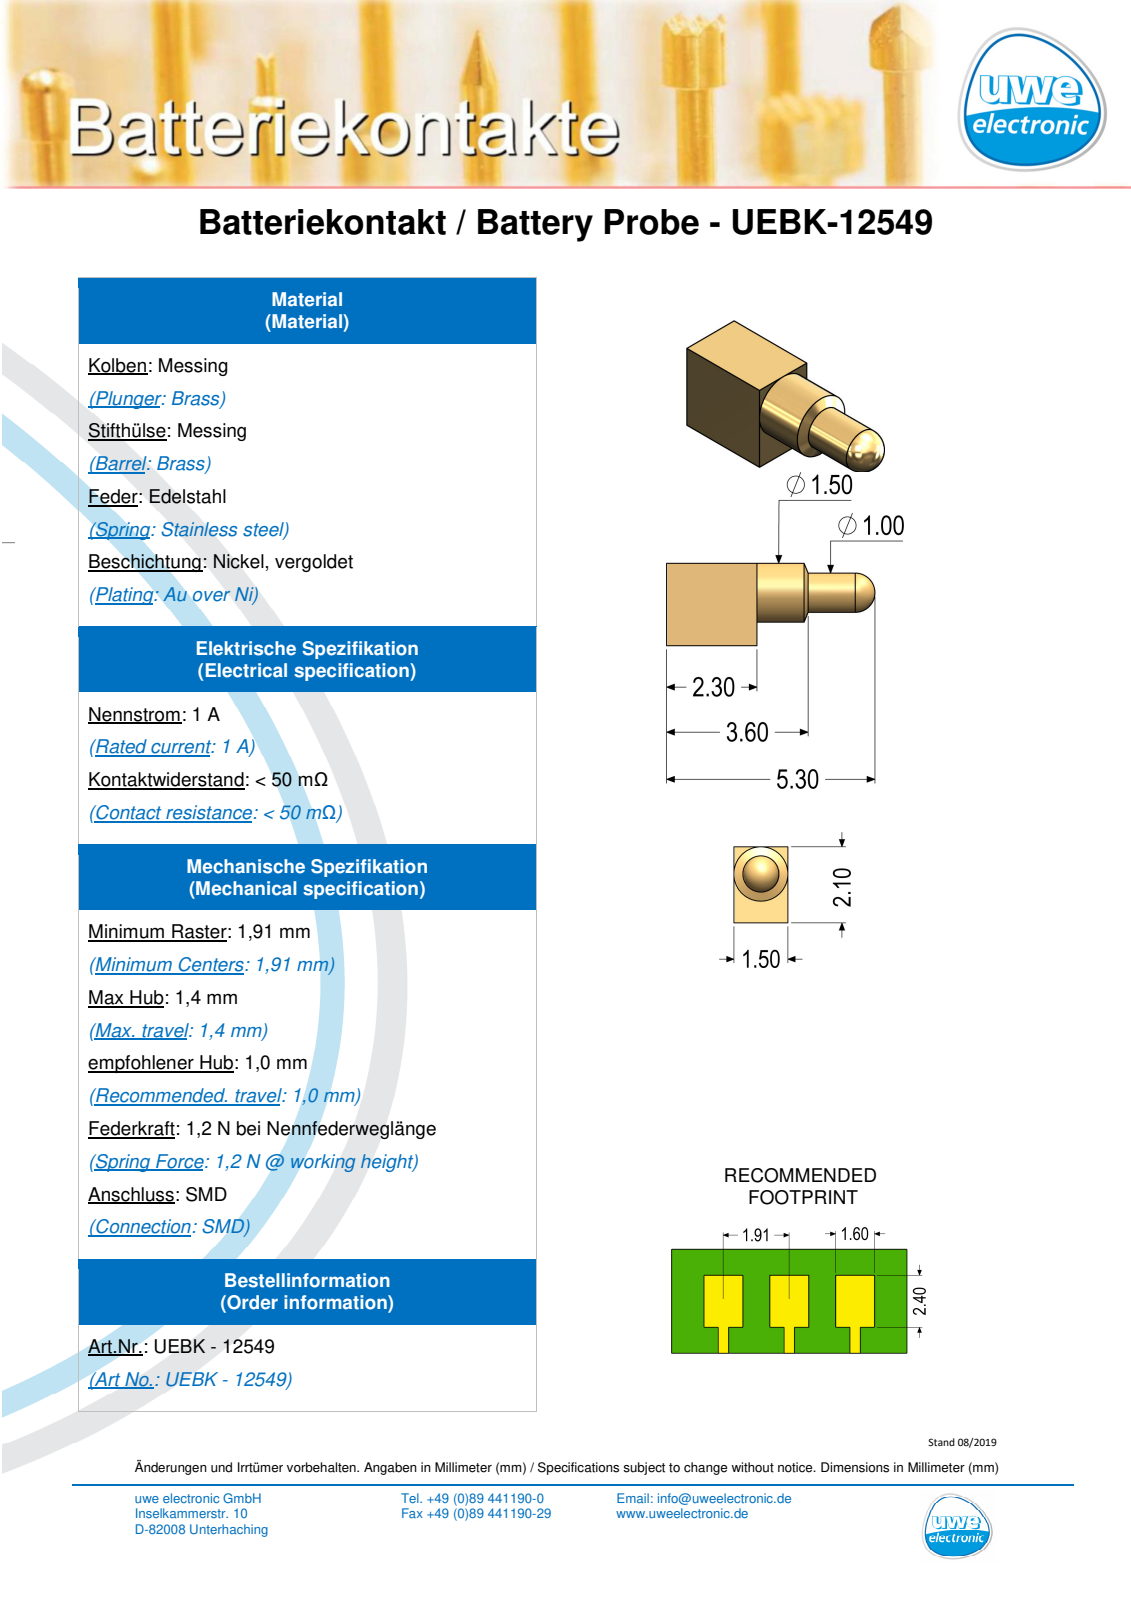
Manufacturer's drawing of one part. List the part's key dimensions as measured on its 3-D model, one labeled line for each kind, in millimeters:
Part name (STEP PRODUCT): UEBK-12549
STEP written by: SolidWorks 2022 (AUTOMOTIVE_DESIGN)
Units: millimetres
Bodies: 1 solid, 16 faces (8 planar, 4 cylindrical, 4 other)
Overall size (bounding box): 5.3 × 2.1 × 1.5
Volume: 11 mm³ · Surface area: 33 mm²
Round bosses / shafts (diameter × count): ⌀1.5 ×1, ⌀1 ×1
Main face-to-face distances: 1.5, 2.1, 2.3
